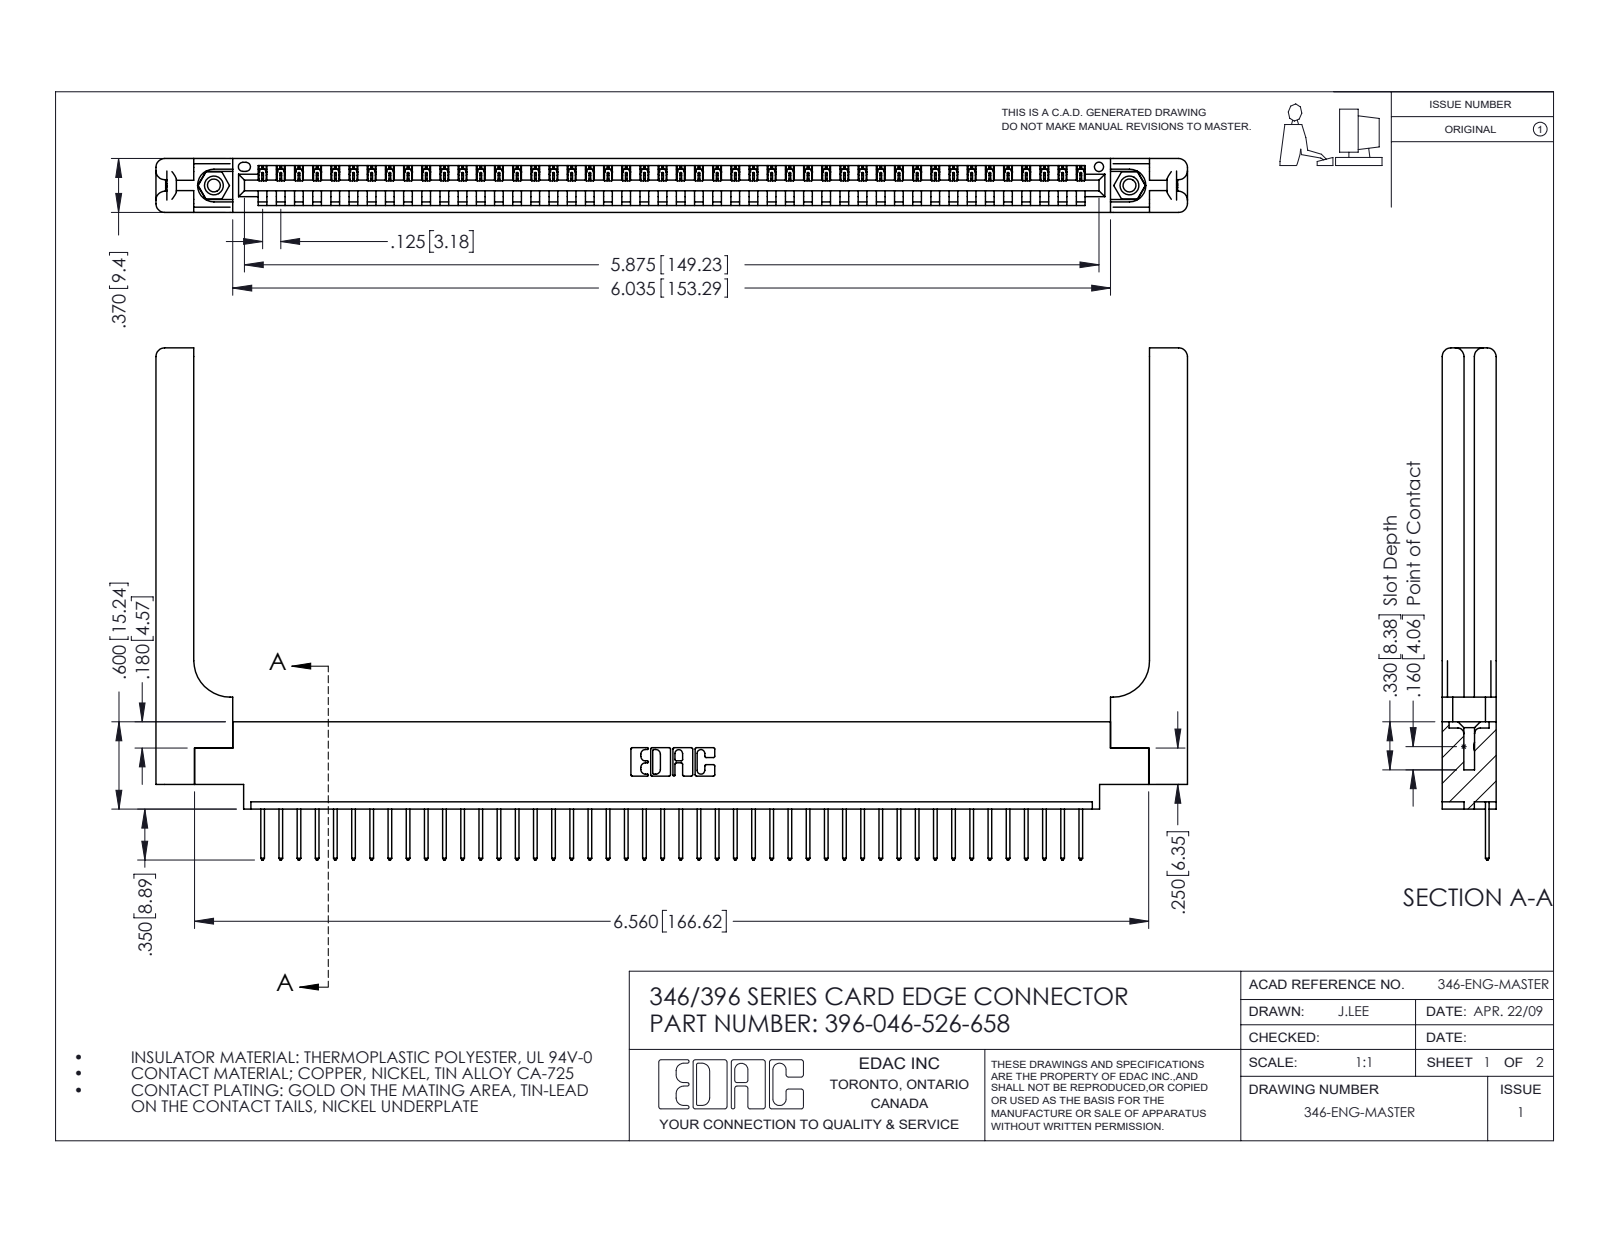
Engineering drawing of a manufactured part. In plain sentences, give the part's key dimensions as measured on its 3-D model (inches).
The part is named "345-292-001_345-293-126; 346-220-058_345-220-058; 346 Part_0.170 Offset - 0.156 Dia-TH; 345-250-001_345-250-001-102 (+1 more)". Its 3-D file was written by "SolidWorks 2016 (CONFIG_CONTROL_DESIGN)". It is 51 solids with 3050 faces: 2068 planar, 922 cylindrical and 60 other. Overall it measures 7.091 by 3.52 by 0.37 inches. Its volume is 1.501 cubic inches and its surface area 41.34 square inches. Round holes: 2 of diameter 0.089, 2 of diameter 0.125, 2 of diameter 0.156, 1 of diameter 0.064. Round bosses or shafts: 2 of diameter 0.155. Partial cylindrical surfaces (rounded edges, fillets, slot ends): 92 of radius 0.006, 92 of radius 0.01, 22 of radius 0.01, 16 of radius 0.06, 6 of radius 0.007, 6 of radius 0.031, 3 of radius 0.026, 2 of radius 0.03. The main face-to-face distances are 0.37, 0.048, 0.322, 0.072, 0.148, 0.15, 0.25, 0.298, 0.025, 0.222. The hole center spacings are 0.246, 6.086, 6.295.
